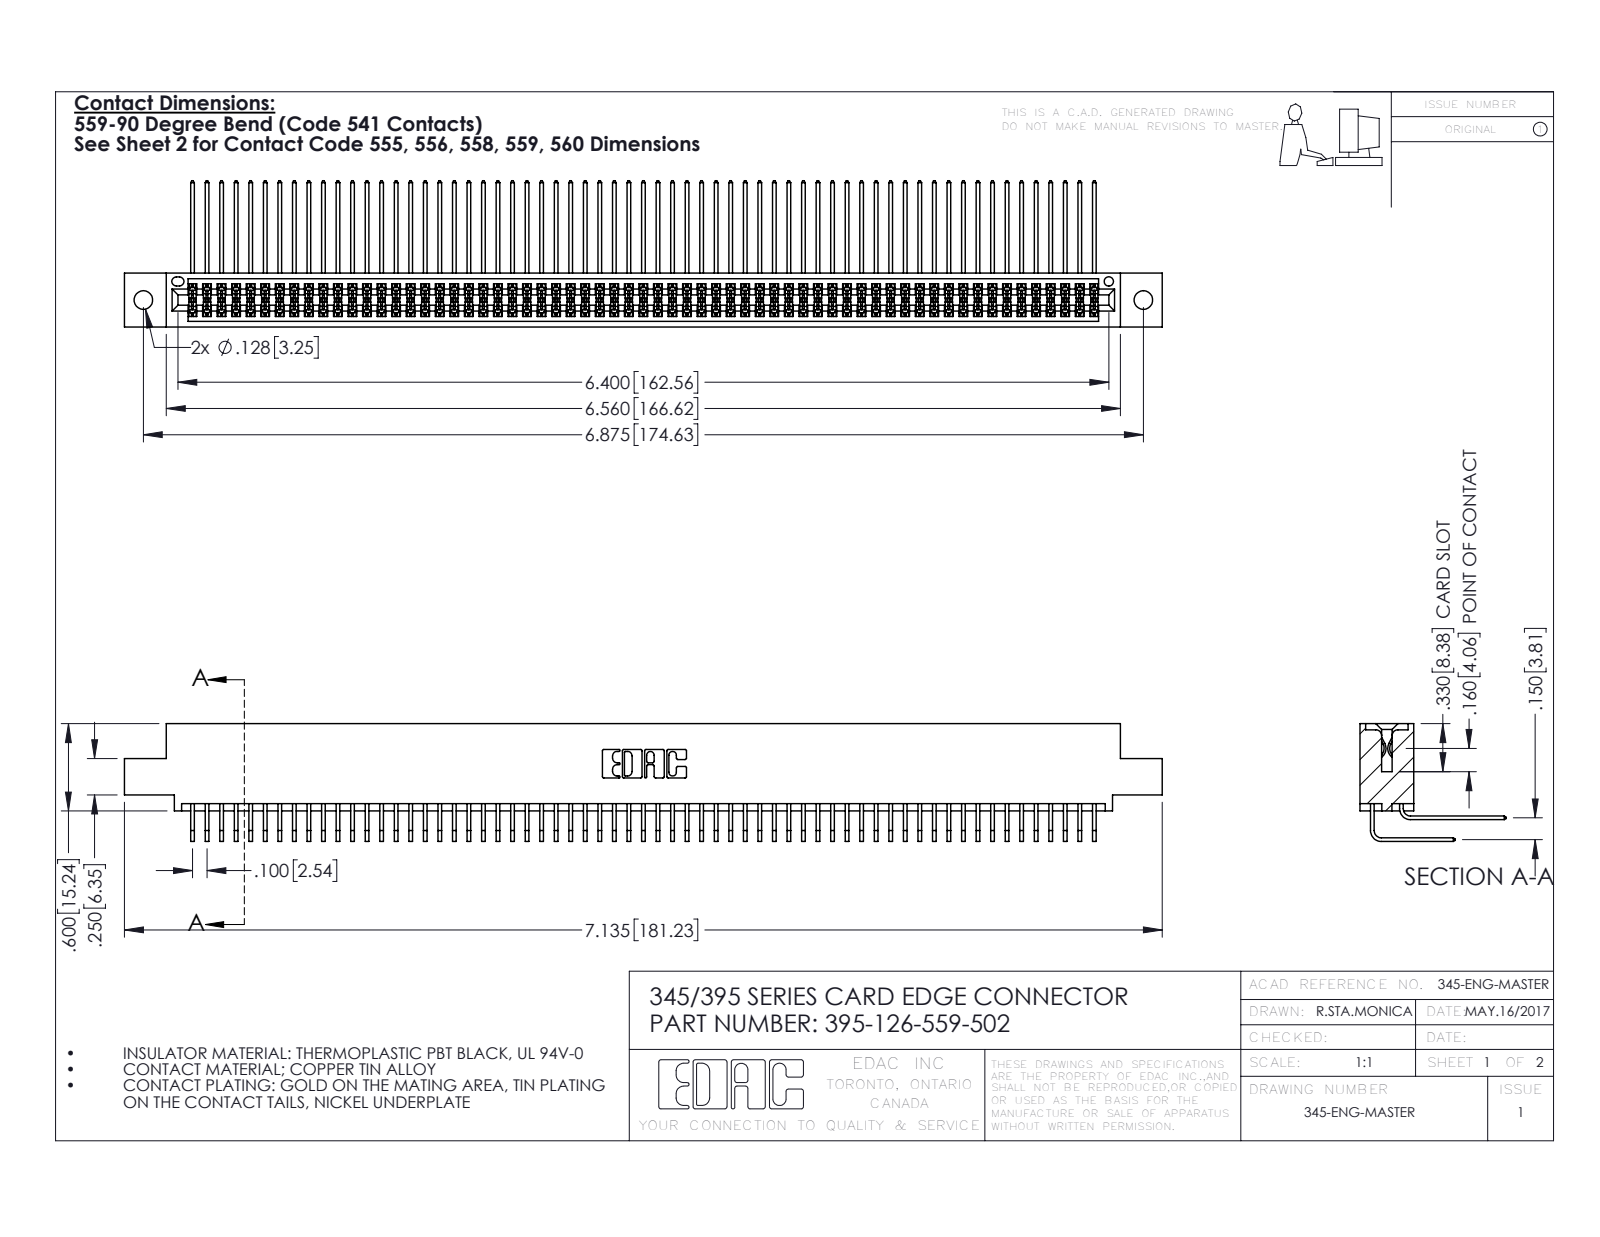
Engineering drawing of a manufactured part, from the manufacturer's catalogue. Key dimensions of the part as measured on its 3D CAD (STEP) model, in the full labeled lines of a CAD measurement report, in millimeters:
Part name (STEP PRODUCT): 345-292-001_558 559 Tail - 1; 345-292-001_559 Tail - 2; 345 Part_0.110 Offset - 0.128 Dia; 395-126-559-502
STEP written by: SolidWorks 2016 (CONFIG_CONTROL_DESIGN)
Units: millimetres
Bodies: 127 solids, 6682 faces (4494 planar, 2188 cylindrical, 0 other)
Overall size (bounding box): 181.2 × 25.5 × 20.5
Volume: 18 420 mm³ · Surface area: 30 860 mm²
Round holes (diameter × count): ⌀3.3 ×2, ⌀1.6 ×1
Partial cylindrical surfaces — rounded edges, fillets, slot ends (radius × count): R0.2 ×190, R0.3 ×22, R0.2 ×6, R0.8 ×6, R0.7 ×3, R0.4 ×2, R0.5 ×2, R0.6 ×2
Main face-to-face distances: 1.8, 7.6, 5.1, 9.4, 2.5, 6.9, 0.6, 5.7, 4.4, 3.8
Hole centre spacings: 6.9, 168.6, 174.6
